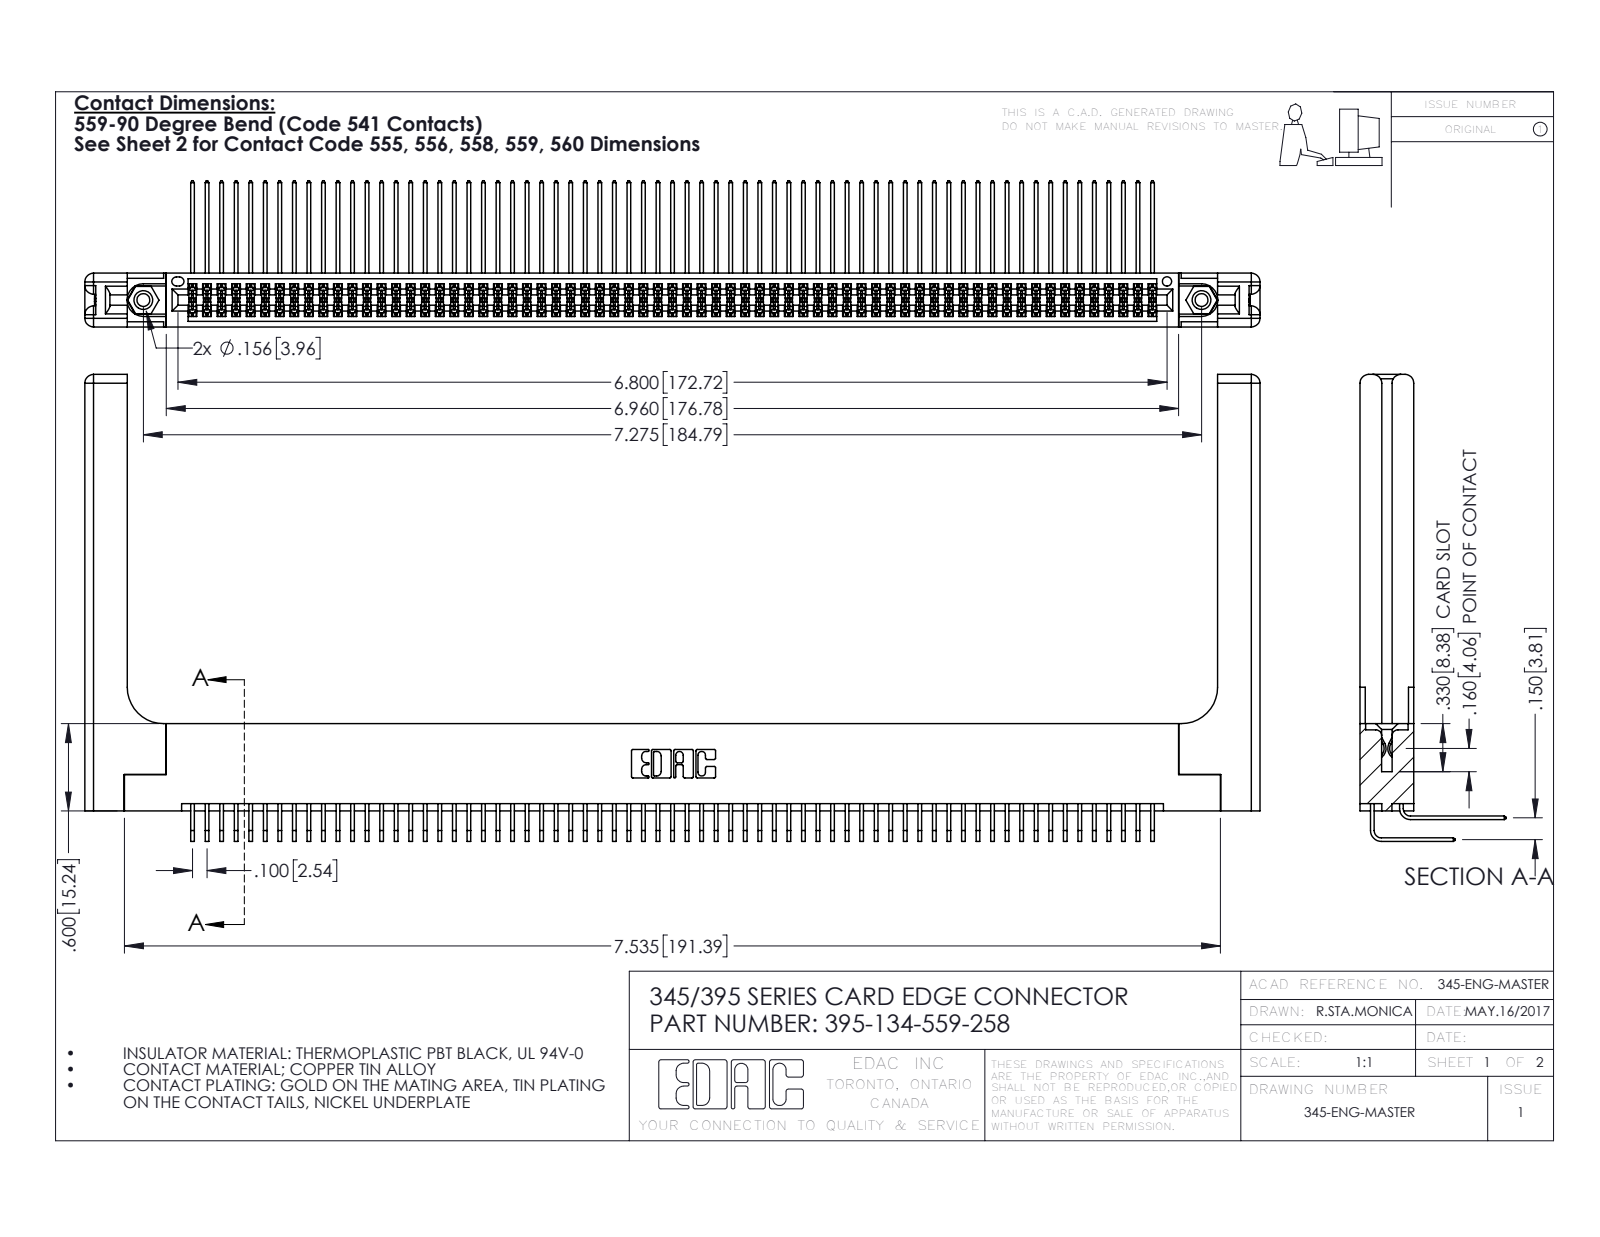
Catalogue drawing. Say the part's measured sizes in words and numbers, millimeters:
The part is named "345-250-001_345-250-001-102; 345 Part_Flush Mounting Lugs - 0.156 Dia-TH; 395-134-559-258; 345-220-058_345-220-058 (+2 more)". Its 3-D file was written by "SolidWorks 2016 (CONFIG_CONTROL_DESIGN)". It is 139 solids with 7350 faces: 4918 planar, 2372 cylindrical and 60 other. Overall it measures 205.2 by 81.5 by 25.5 millimeters. Its volume is 29 410 cubic millimeters and its surface area 40 130 square millimeters. Round holes: 2 of diameter 2.3, 2 of diameter 3.2, 2 of diameter 4, 1 of diameter 1.6. Round bosses or shafts: 2 of diameter 3.9. Partial cylindrical surfaces (rounded edges, fillets, slot ends): 202 of radius 0.2, 22 of radius 0.3, 16 of radius 1.5, 6 of radius 0.2, 6 of radius 0.8, 3 of radius 0.7, 2 of radius 0.4, 2 of radius 0.5. The main face-to-face distances are 1.8, 7.6, 9.4, 5.1, 2.5, 6.9, 0.6, 5.7, 4.4, 3.8. The hole center spacings are 6.9, 178.8, 184.8.
